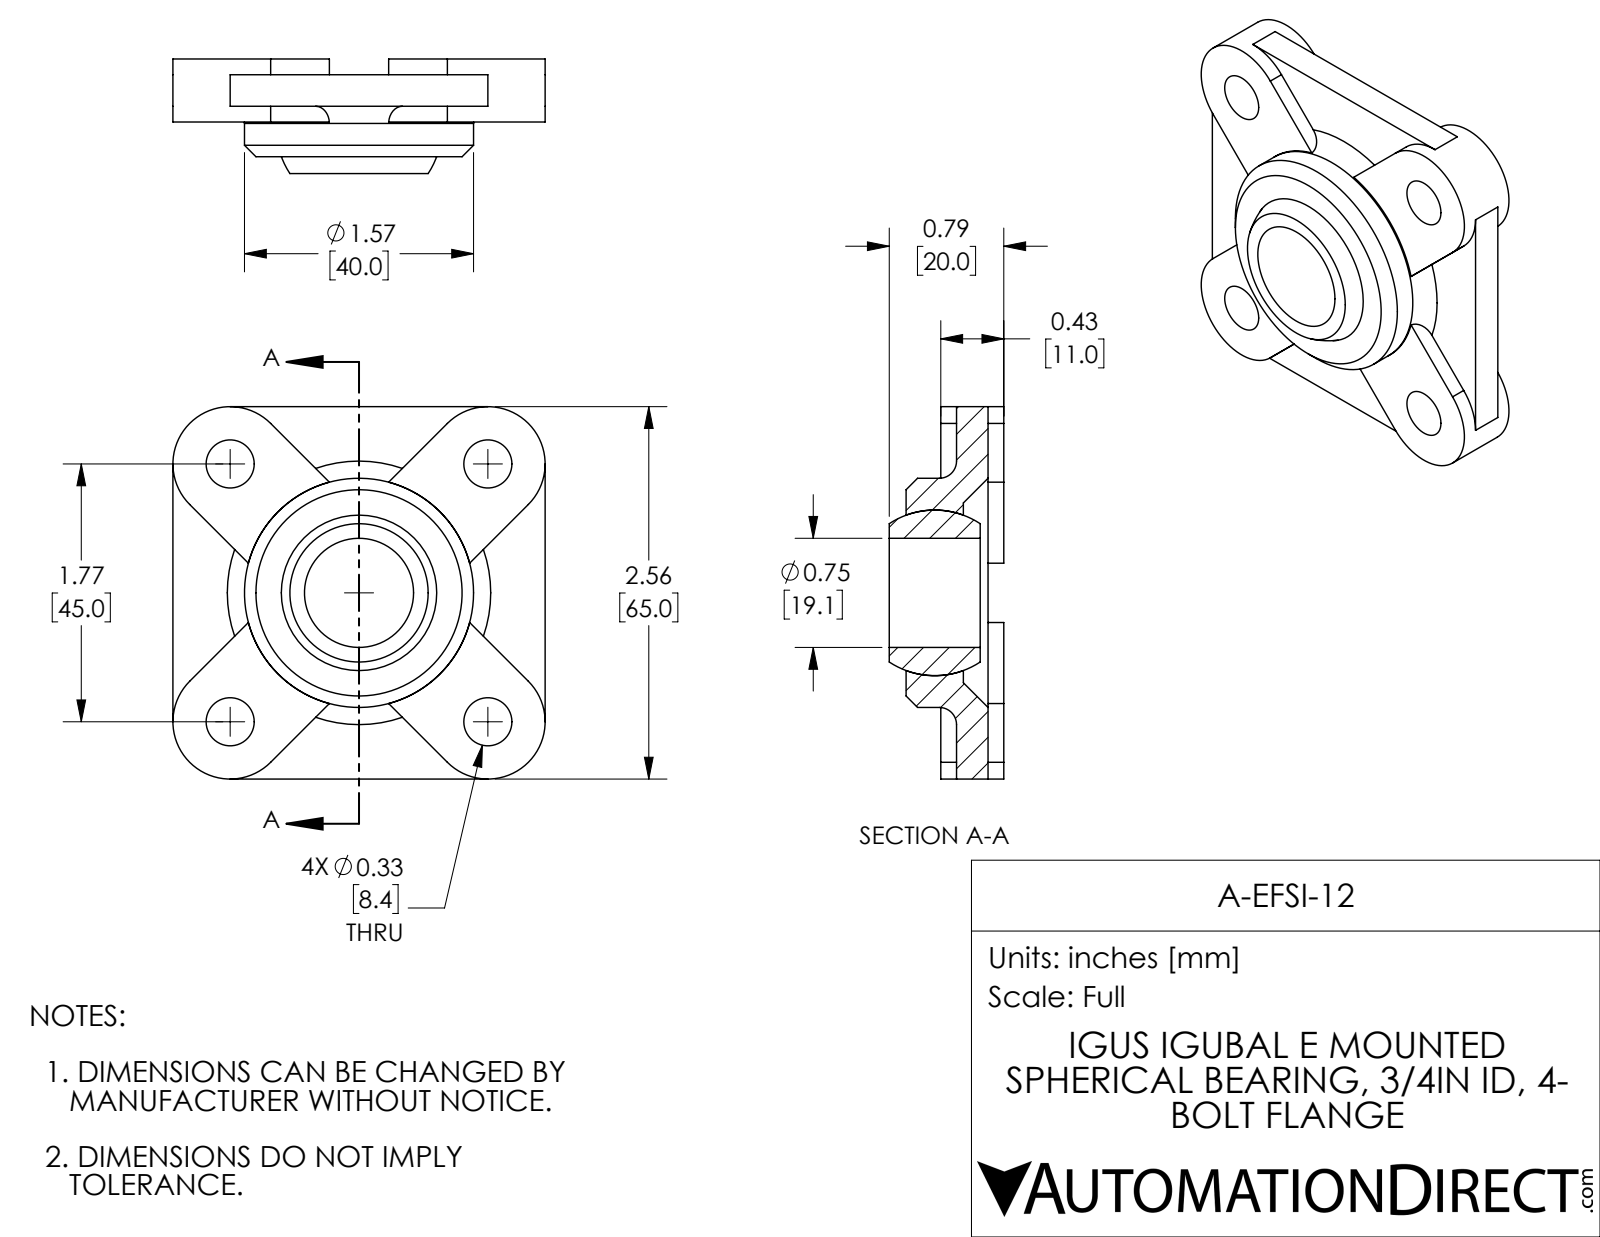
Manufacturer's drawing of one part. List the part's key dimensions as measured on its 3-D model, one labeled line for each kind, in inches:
Part name (STEP PRODUCT): A-EFSI-12
STEP written by: SolidWorks 2017 (AUTOMOTIVE_DESIGN)
Units: inches
Bodies: 2 solids, 74 faces (40 planar, 24 cylindrical, 10 other)
Overall size (bounding box): 2.559 × 2.559 × 1.021
Volume: 2.104 in³ · Surface area: 23.62 in²
Round holes (diameter × count): ⌀0.331 ×4, ⌀0.75 ×1, ⌀1.575 ×1
Partial cylindrical surfaces — rounded edges, fillets, slot ends (radius × count): R0.394 ×4
Main face-to-face distances: 0.108, 0.325, 0.433, 0.217, 2.559, 0.787, 0.672, 0.563, 0.347, 0.239
Hole centre spacings: 1.253, 1.772, 2.506
